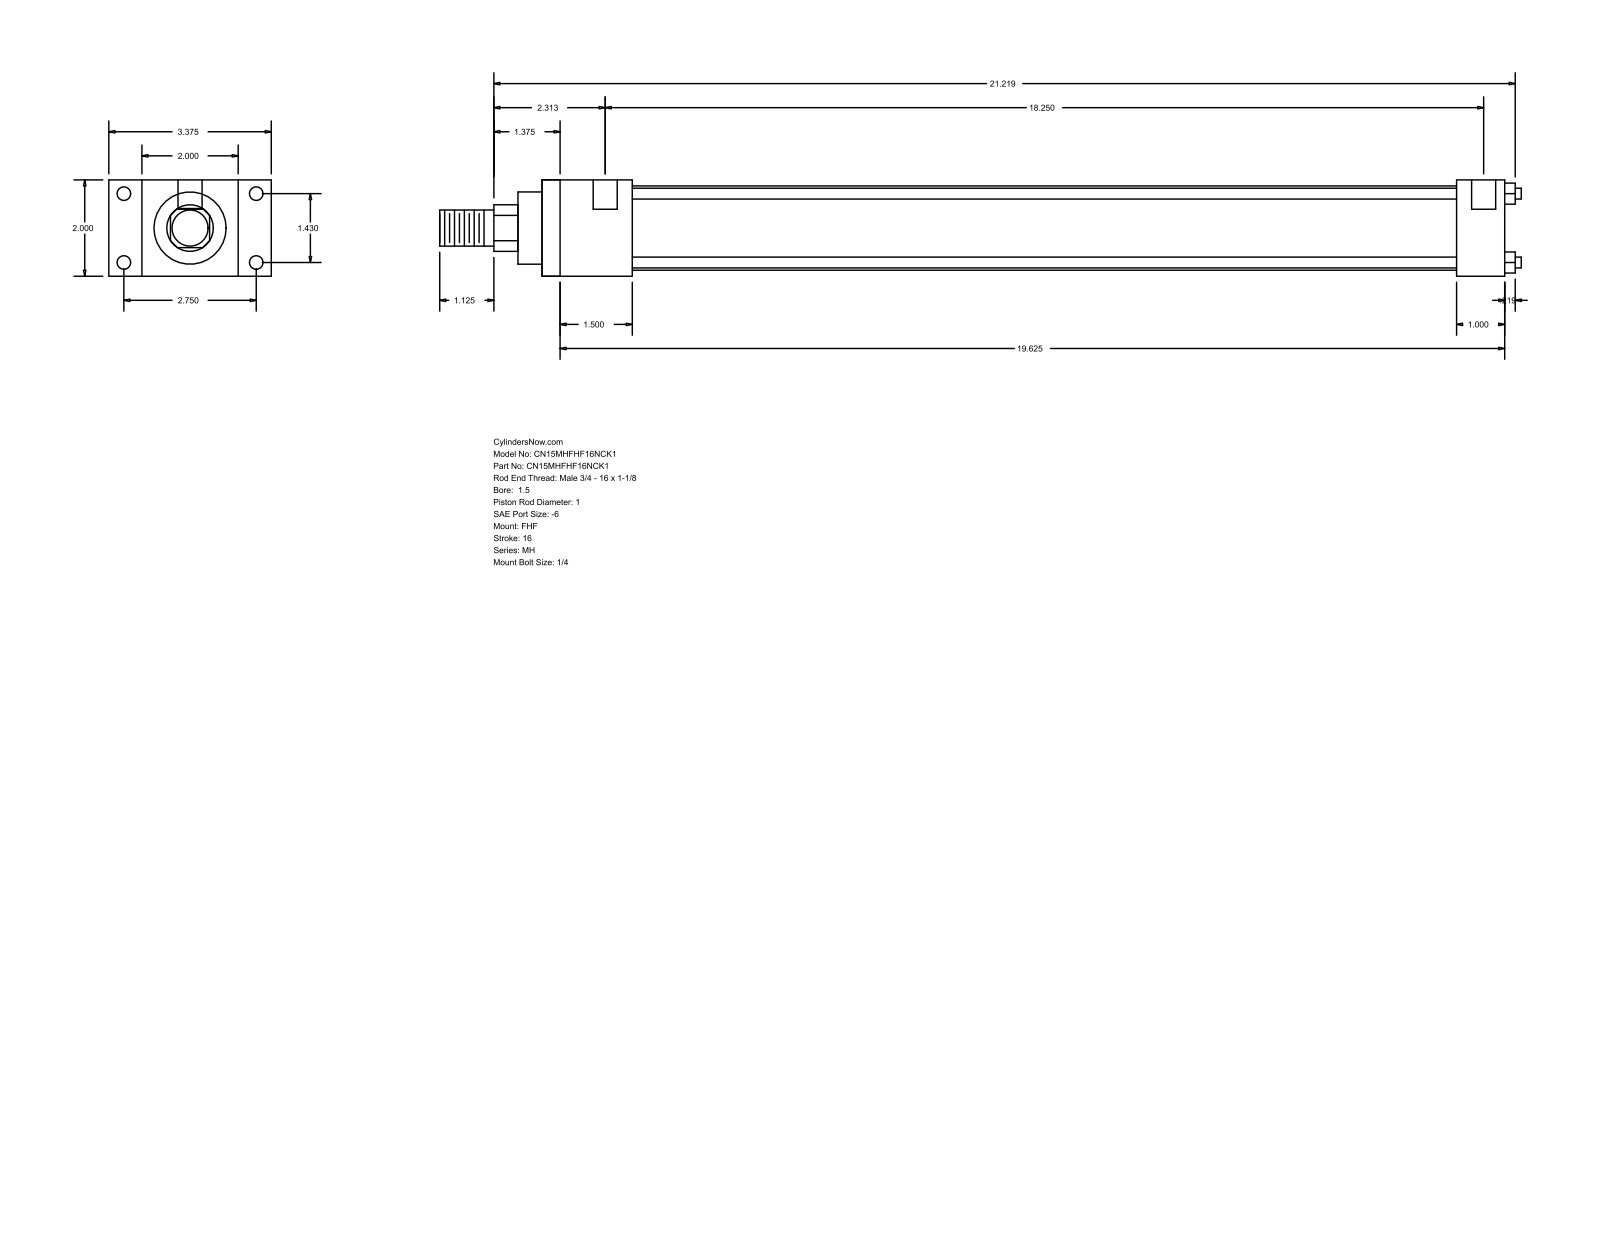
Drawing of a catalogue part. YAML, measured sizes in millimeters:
part_name: "MH_FHF__0150_1"
step_written_by: "GSSL Pune (CONFIG_CONTROL_DESIGN)"
units: millimeters
bodies: {solids: 0, faces: 88, planar: 60, cylindrical: 28, other: 0}
overall_size: [570.71, 85.72, 50.8]
round_holes:
  - {diameter: 5.56, count: 4}
  - {diameter: 7.14, count: 4}
  - {diameter: 12.7, count: 2}
round_bosses_or_shafts:
  - {diameter: 5.71, count: 4}
  - {diameter: 44.45, count: 1}
  - {diameter: 38.1, count: 1}
  - {diameter: 25.4, count: 1}
  - {diameter: 19.05, count: 1}
partial_cylinders:
  - {radius: 12.29, count: 1}
face_to_face_distances: [50.8, 17.46, 68.26, 47.63, 85.72, 508, 460.37, 25.4, 482.6, 434.97]
hole_center_spacings: [36.32, 69.84, 78.72, 466.73, 3.18, 463.55]
